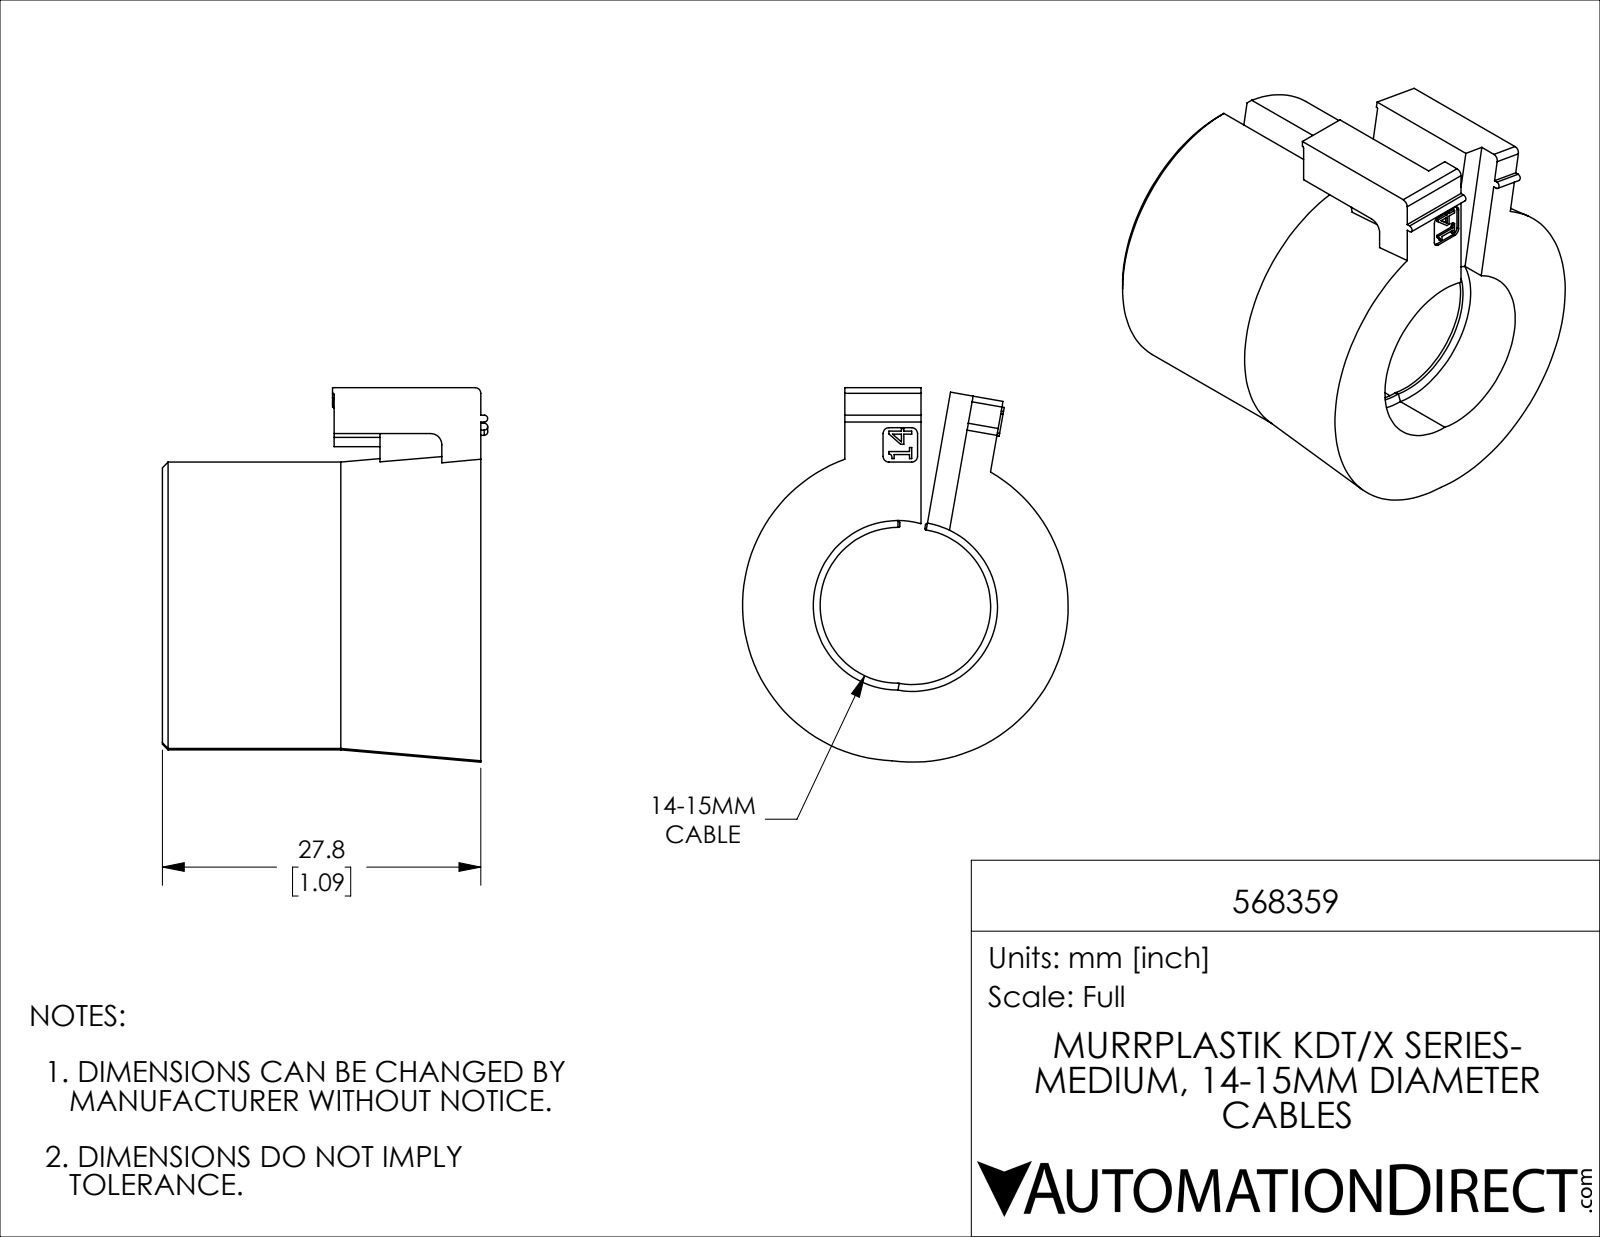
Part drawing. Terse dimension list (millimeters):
name: 568359
written by: SolidWorks 2019 (CONFIG_CONTROL_DESIGN)
unit: mm
bodies: 1 solid, 129 faces (86 planar, 29 cylindrical, 14 other)
size: 32.7 × 28.4 × 28.4
volume: 9 930 mm³; area: 5 082 mm²
rounds: 6× R0.1, 6× R0.5, 2× R0.3, 2× R1, 2× R6.8, 2× R7.4, 2× R12.5
face distances: 27.8, 2, 4, 4.6, 4.6, 25.8, 12.8, 10.8, 15, 2.6
